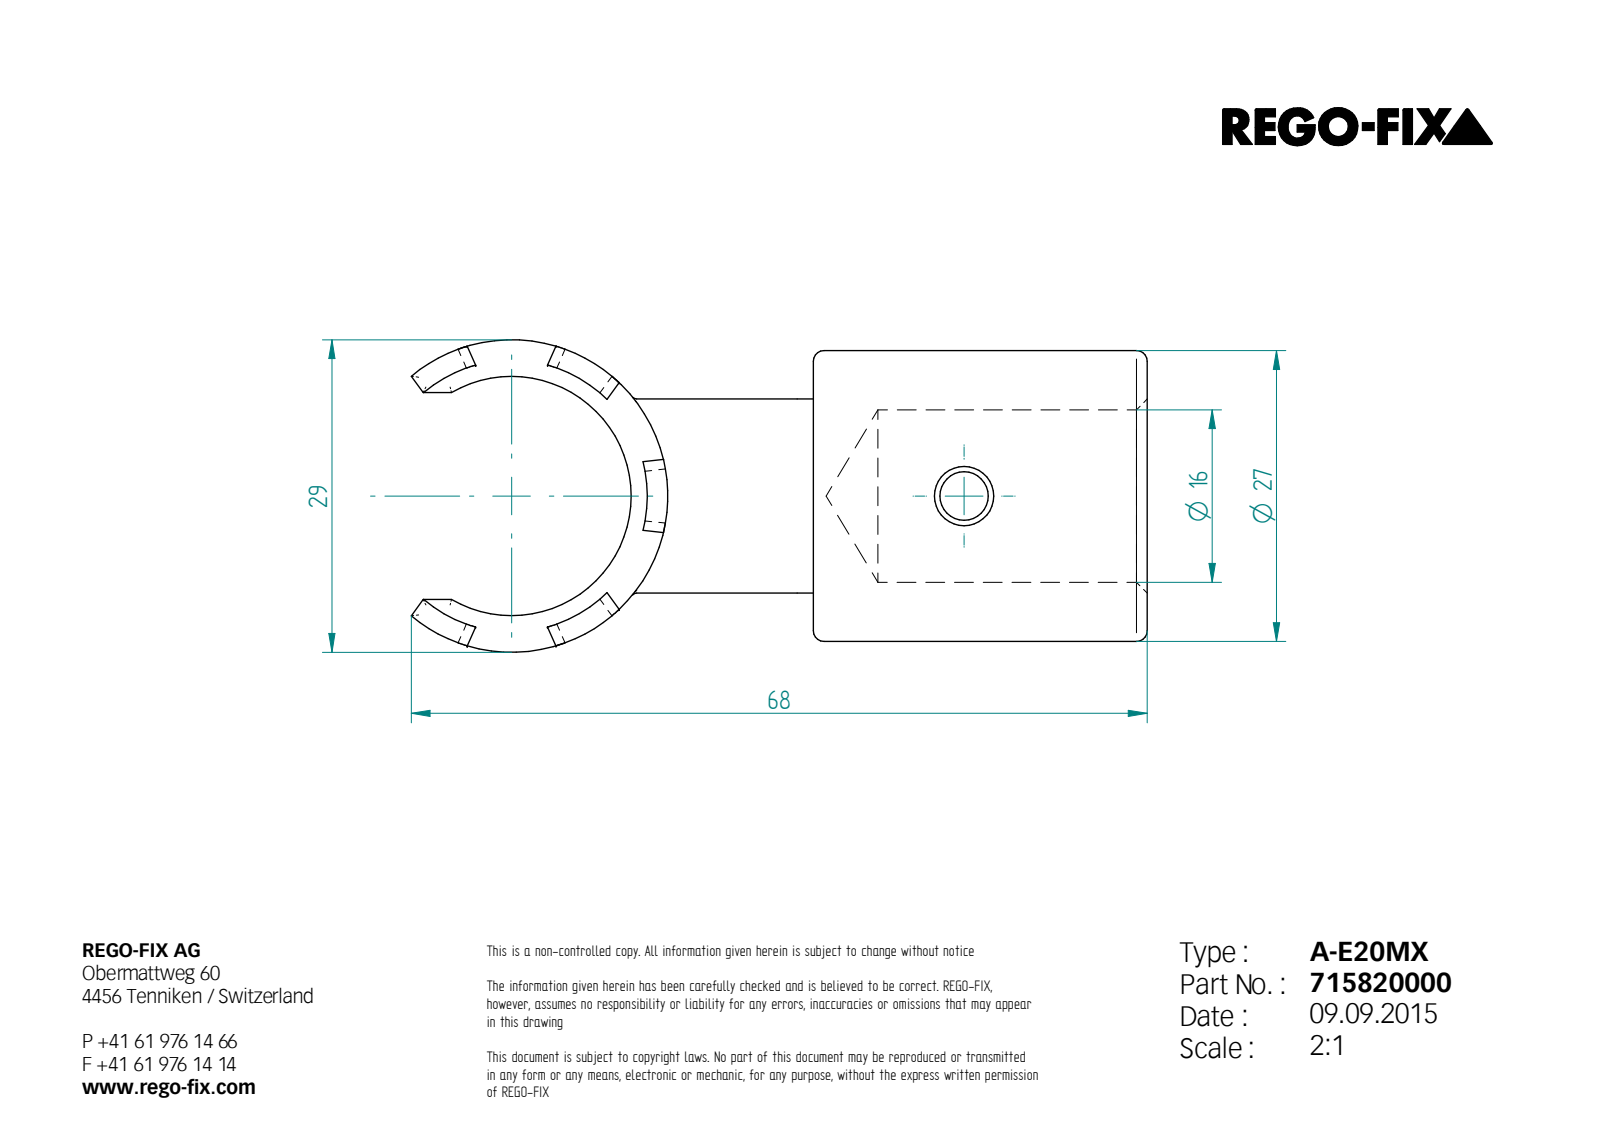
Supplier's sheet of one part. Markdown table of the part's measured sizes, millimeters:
| quantity | value |
| --- | --- |
| STEP written by | Unknown (AUTOMOTIVE_DESIGN) |
| units | millimeters |
| bodies | 1 solid, 72 faces (26 planar, 29 cylindrical, 17 other) |
| overall size | 68.31 × 29 × 27 |
| volume | 14 418 mm³ |
| surface area | 6 943 mm² |
| round holes (diameter × count) | 4.5 × 1, 5.5 × 1, 16 × 1 |
| round bosses / shafts (diameter × count) | 27 × 1 |
| partial cylindrical surfaces (radius × count) | 0.9 × 8, 0.5 × 4, 1.5 × 2, 2 × 2, 4 × 1, 11.1 × 1, 12.6 × 1, 14.5 × 1 |
| main face-to-face distances | 31, 4, 2.6, 6.6, 3.4, 6, 10, 19.2, 2, 5.6 |
